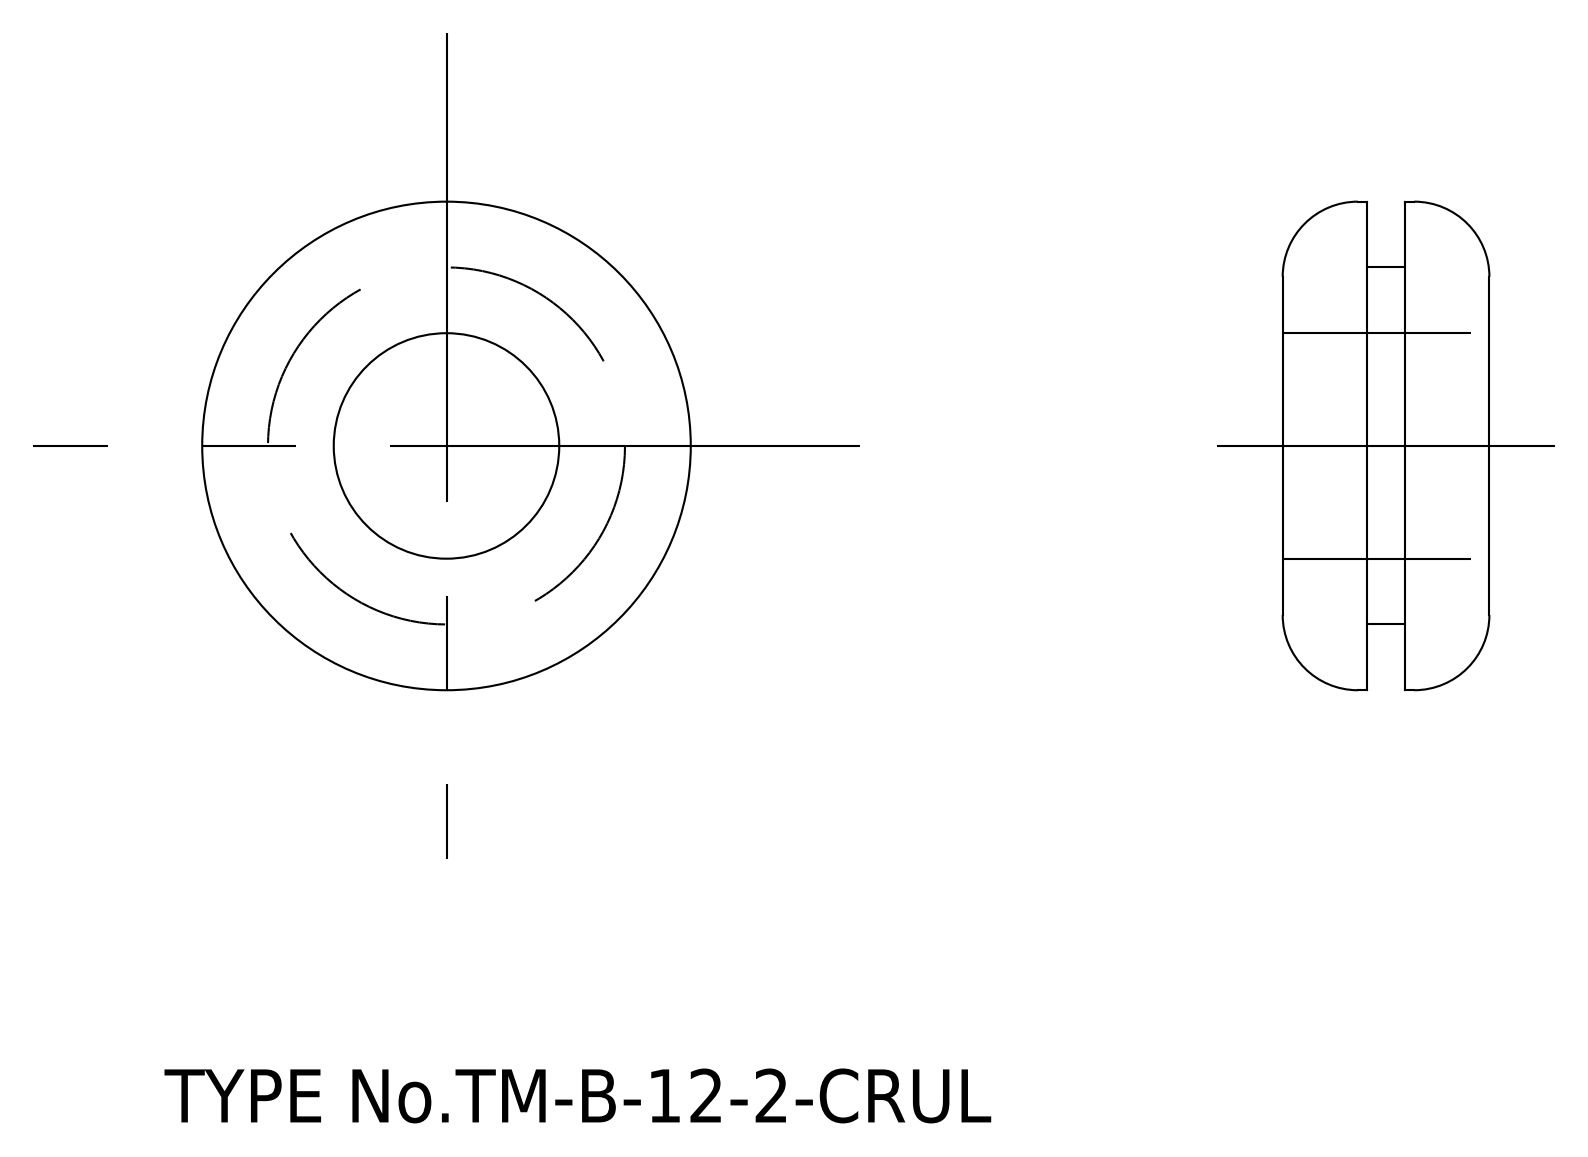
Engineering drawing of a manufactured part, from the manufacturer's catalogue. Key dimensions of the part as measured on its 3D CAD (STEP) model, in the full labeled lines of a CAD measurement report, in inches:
STEP written by: spGate 15.6.1 (AUTOMOTIVE_DESIGN)
Units: inches
Bodies: 1 solid, 16 faces (4 planar, 8 cylindrical, 4 other)
Overall size (bounding box): 1.024 × 1.024 × 0.433
Volume: 0.218 in³ · Surface area: 3.573 in²
Round holes (diameter × count): ⌀0.472 ×1
Round bosses / shafts (diameter × count): ⌀1.024 ×1, ⌀0.748 ×1
Main face-to-face distances: 0.177, 0.256, 0.079, 0.433
